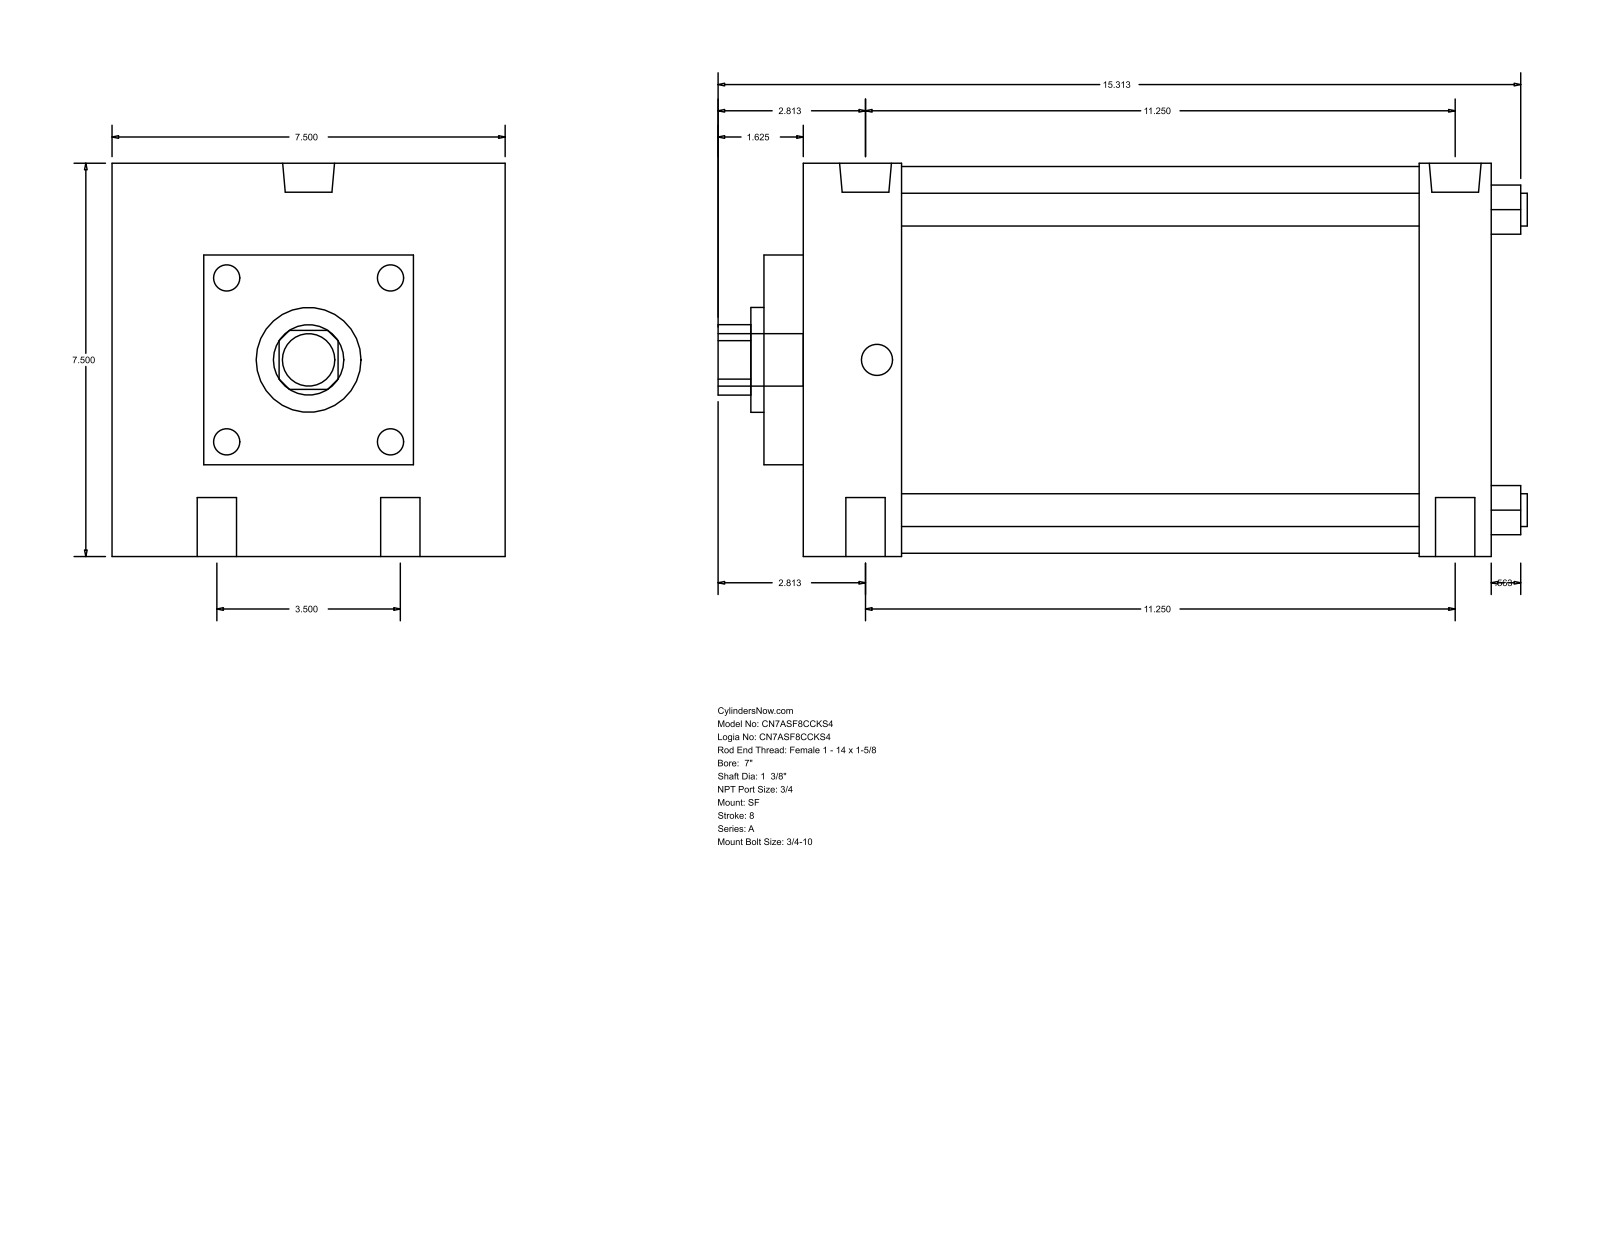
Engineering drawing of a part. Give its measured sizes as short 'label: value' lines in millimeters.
name: A_SF__0700_1.375
written by: GSSL Pune (CONFIG_CONTROL_DESIGN)
unit: mm
bodies: 0 solids, 93 faces (67 planar, 26 cylindrical, 0 other)
size: 392.11 × 190.5 × 190.5
holes: 4× ⌀19.05, 2× ⌀15.08, 2× ⌀25.12, 1× ⌀34.92, 1× ⌀50.8
bosses: 4× ⌀15.88, 1× ⌀187.32, 1× ⌀25.4
rounds: 1× R17.06
face distances: 190.5, 333.38, 19.04, 352.42, 66.67, 317.5, 47.63, 298.46, 250.83, 285.75
hole spacings: 44.45, 289.19, 285.75, 88.9, 299.26, 274.63
